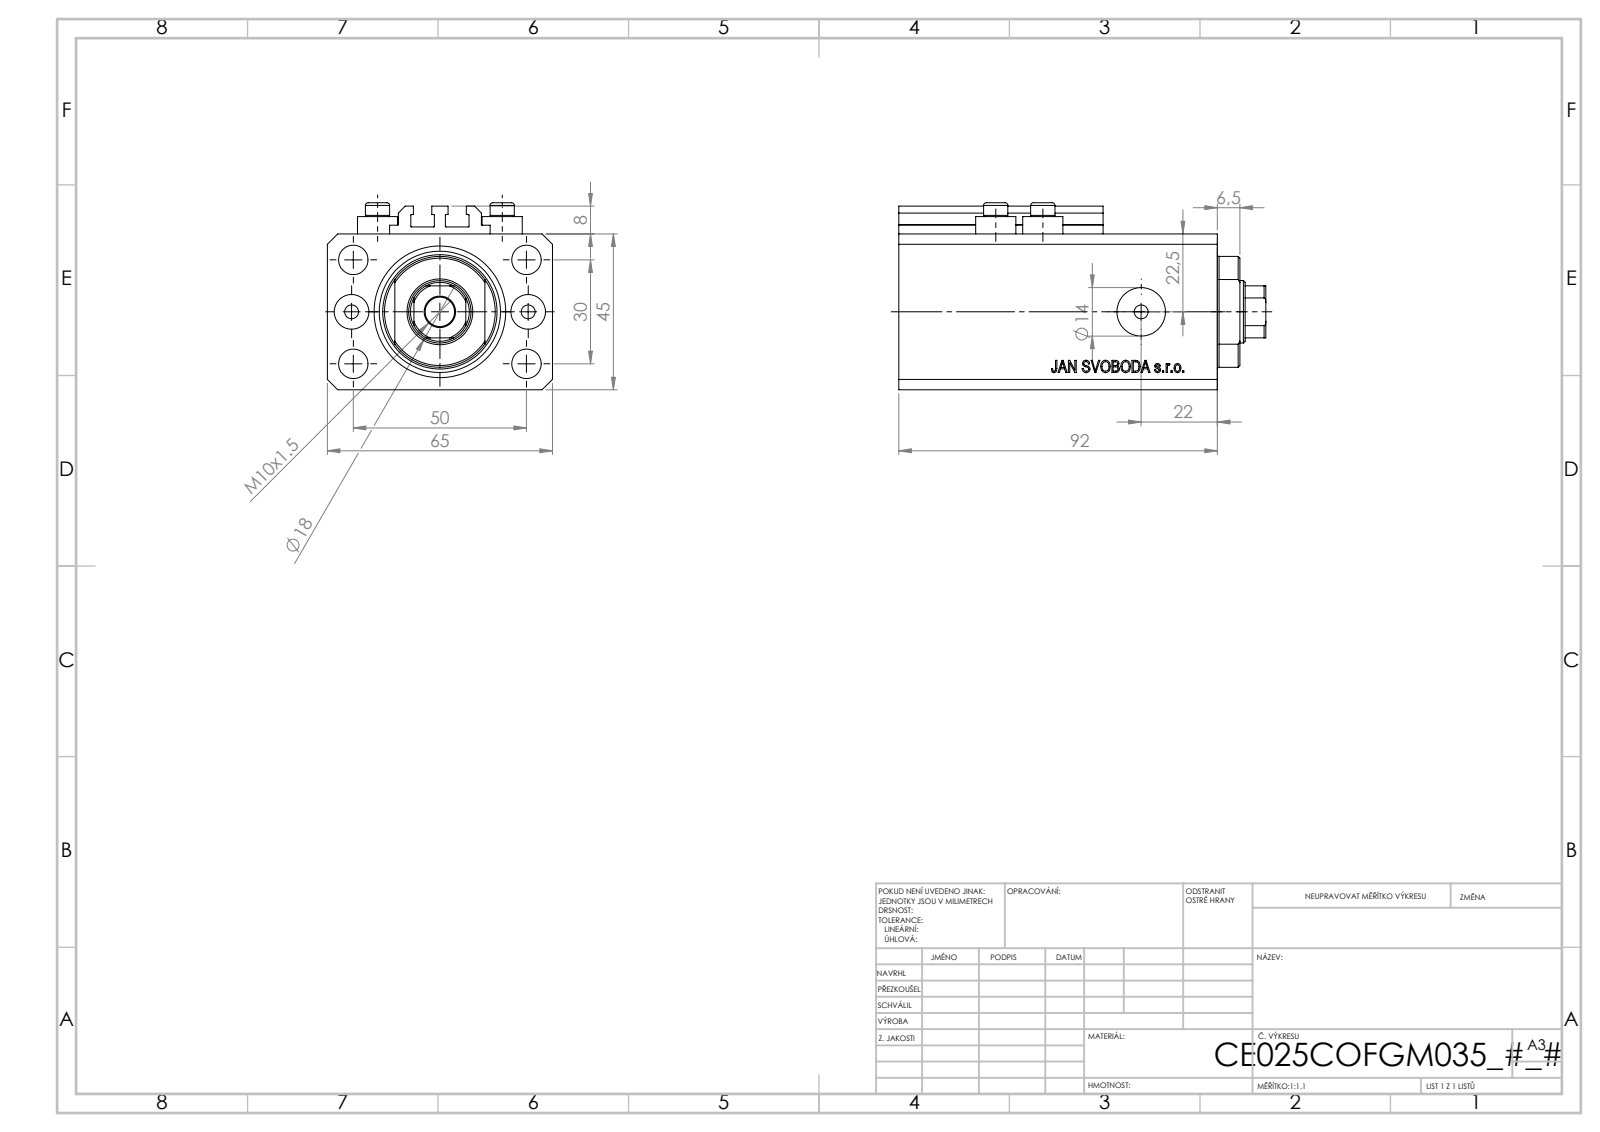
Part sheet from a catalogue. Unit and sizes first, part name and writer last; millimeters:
Units: millimetres
Overall size (bounding box): 106 × 65 × 54
Round holes (diameter × count): ⌀4 ×8, ⌀8.5 ×5, ⌀10 ×2, ⌀14 ×2, ⌀18 ×1, ⌀25 ×1, ⌀38 ×1
Round bosses / shafts (diameter × count): ⌀11.6 ×4, ⌀7 ×4
Partial cylindrical surfaces — rounded edges, fillets, slot ends (radius × count): R0.2 ×10, R8.5 ×1, R16 ×1
Main face-to-face distances: 45, 65, 14, 78, 92, 47, 6.9, 71.1, 85.1, 3
Hole centre spacings: 15.01, 29.15, 52.68, 13.6, 25.5, 30, 36, 38.48
Volume: 250 486 mm³ · Surface area: 65 601 mm²
Bodies: 8 solids, 1034 faces (504 planar, 86 cylindrical, 444 other)
Part name (STEP PRODUCT): V250CE_C_Body; V250CE_VC_C; V250CE_C_VCP; ALLEN BOLT V250CE
STEP written by: SolidWorks 2019 (CONFIG_CONTROL_DESIGN)
